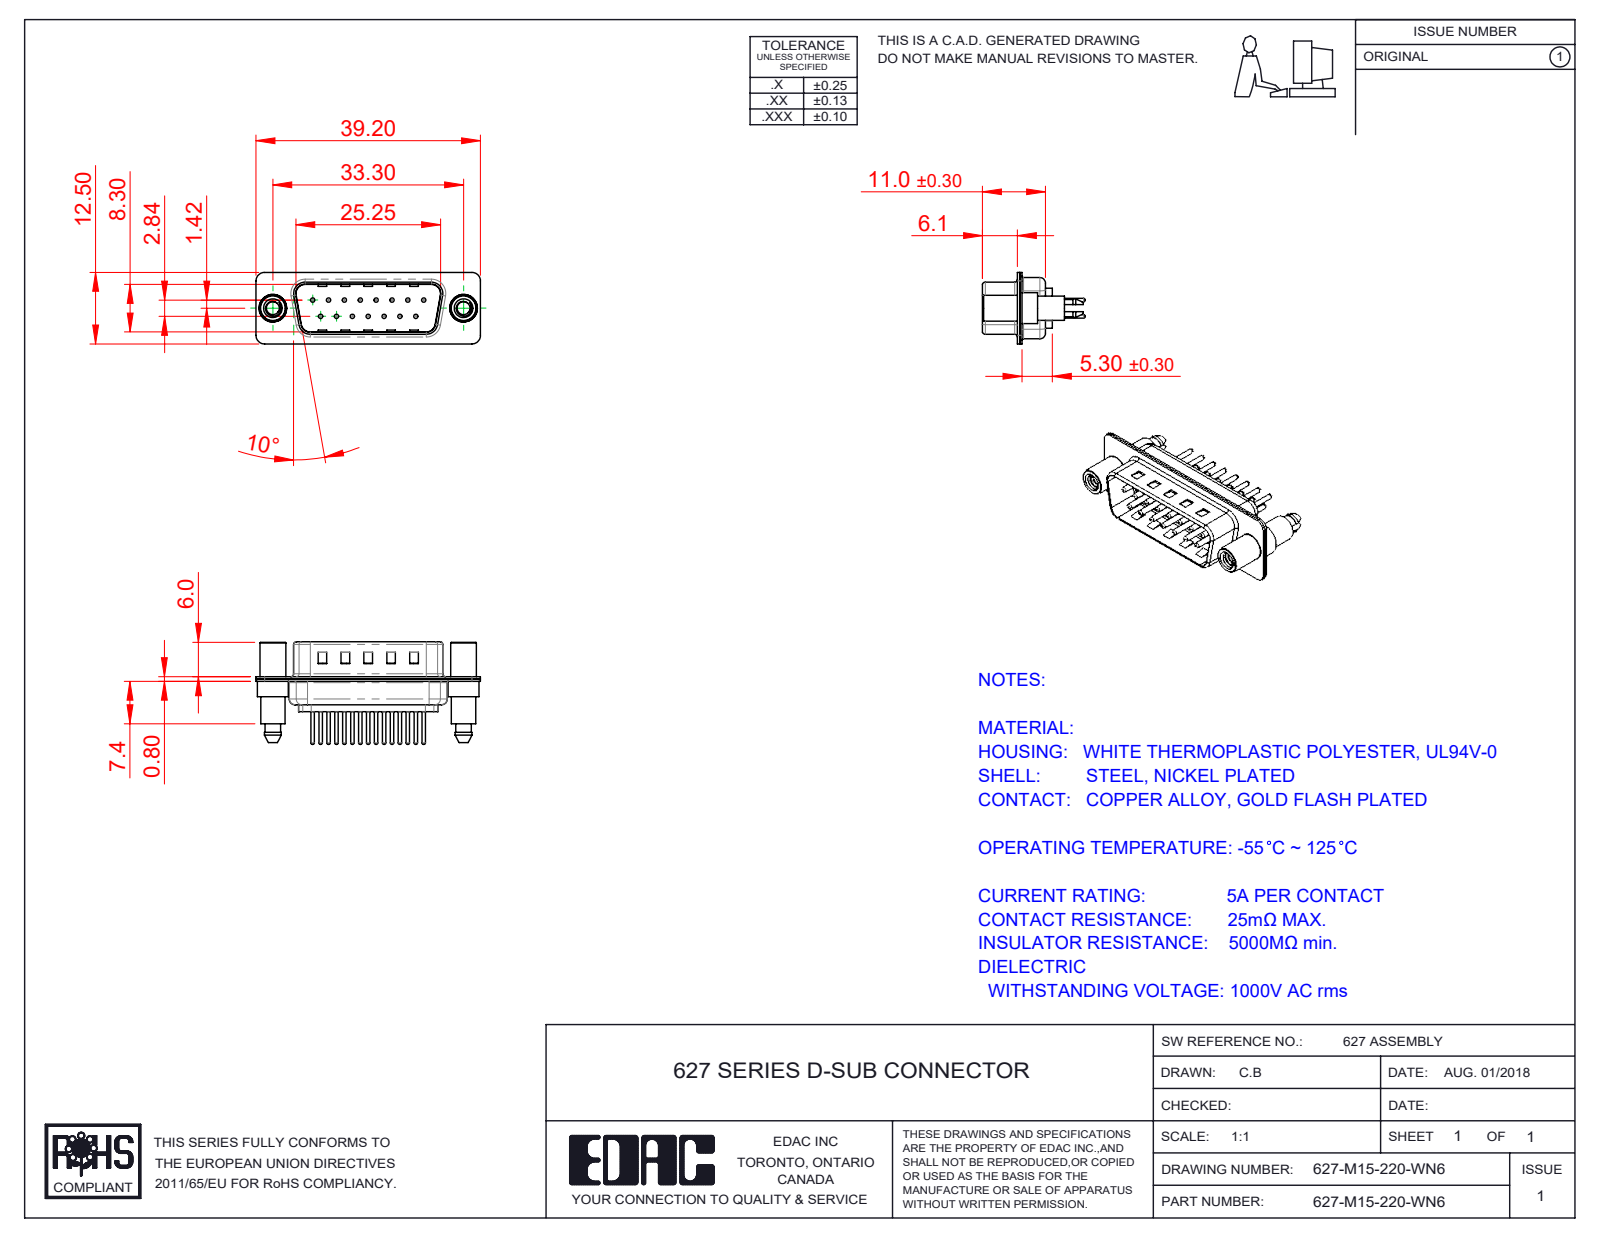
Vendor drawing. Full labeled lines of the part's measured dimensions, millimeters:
Part name (STEP PRODUCT): 627M Shell Front_15 Contacts; 627M Contact Row 2_20; 627M 4-40 Threaded Standoff and Boardlock; 627M Contact Row 1_20 (+3 more)
STEP written by: SolidWorks 2020 (CONFIG_CONTROL_DESIGN)
Units: millimetres
Bodies: 20 solids, 947 faces (262 planar, 371 cylindrical, 314 other)
Overall size (bounding box): 39.2 × 17.9 × 12.5
Volume: 2 182 mm³ · Surface area: 5 276 mm²
Round holes (diameter × count): ⌀0.75 ×15, ⌀1.6 ×15, ⌀2 ×15, ⌀2.26 ×2, ⌀4 ×2, ⌀4.8 ×2
Round bosses / shafts (diameter × count): ⌀1.5 ×15, ⌀0.6 ×15, ⌀5.4 ×2, ⌀4.9 ×2, ⌀4.5 ×2, ⌀4.25 ×2
Partial cylindrical surfaces — rounded edges, fillets, slot ends (radius × count): R1.5 ×18, R2 ×12, R1.6 ×10, R0.5 ×8, R0.25 ×4, R0.6 ×4, R0.65 ×4, R0.9 ×4
Main face-to-face distances: 0.4, 0.8, 9.5, 9.1, 8.7, 9.9, 5.3, 1.2, 6.1, 5.7
Hole centre spacings: 3.16, 2.77, 5.54, 8.31, 11.08, 5.03, 5.04, 7.48
